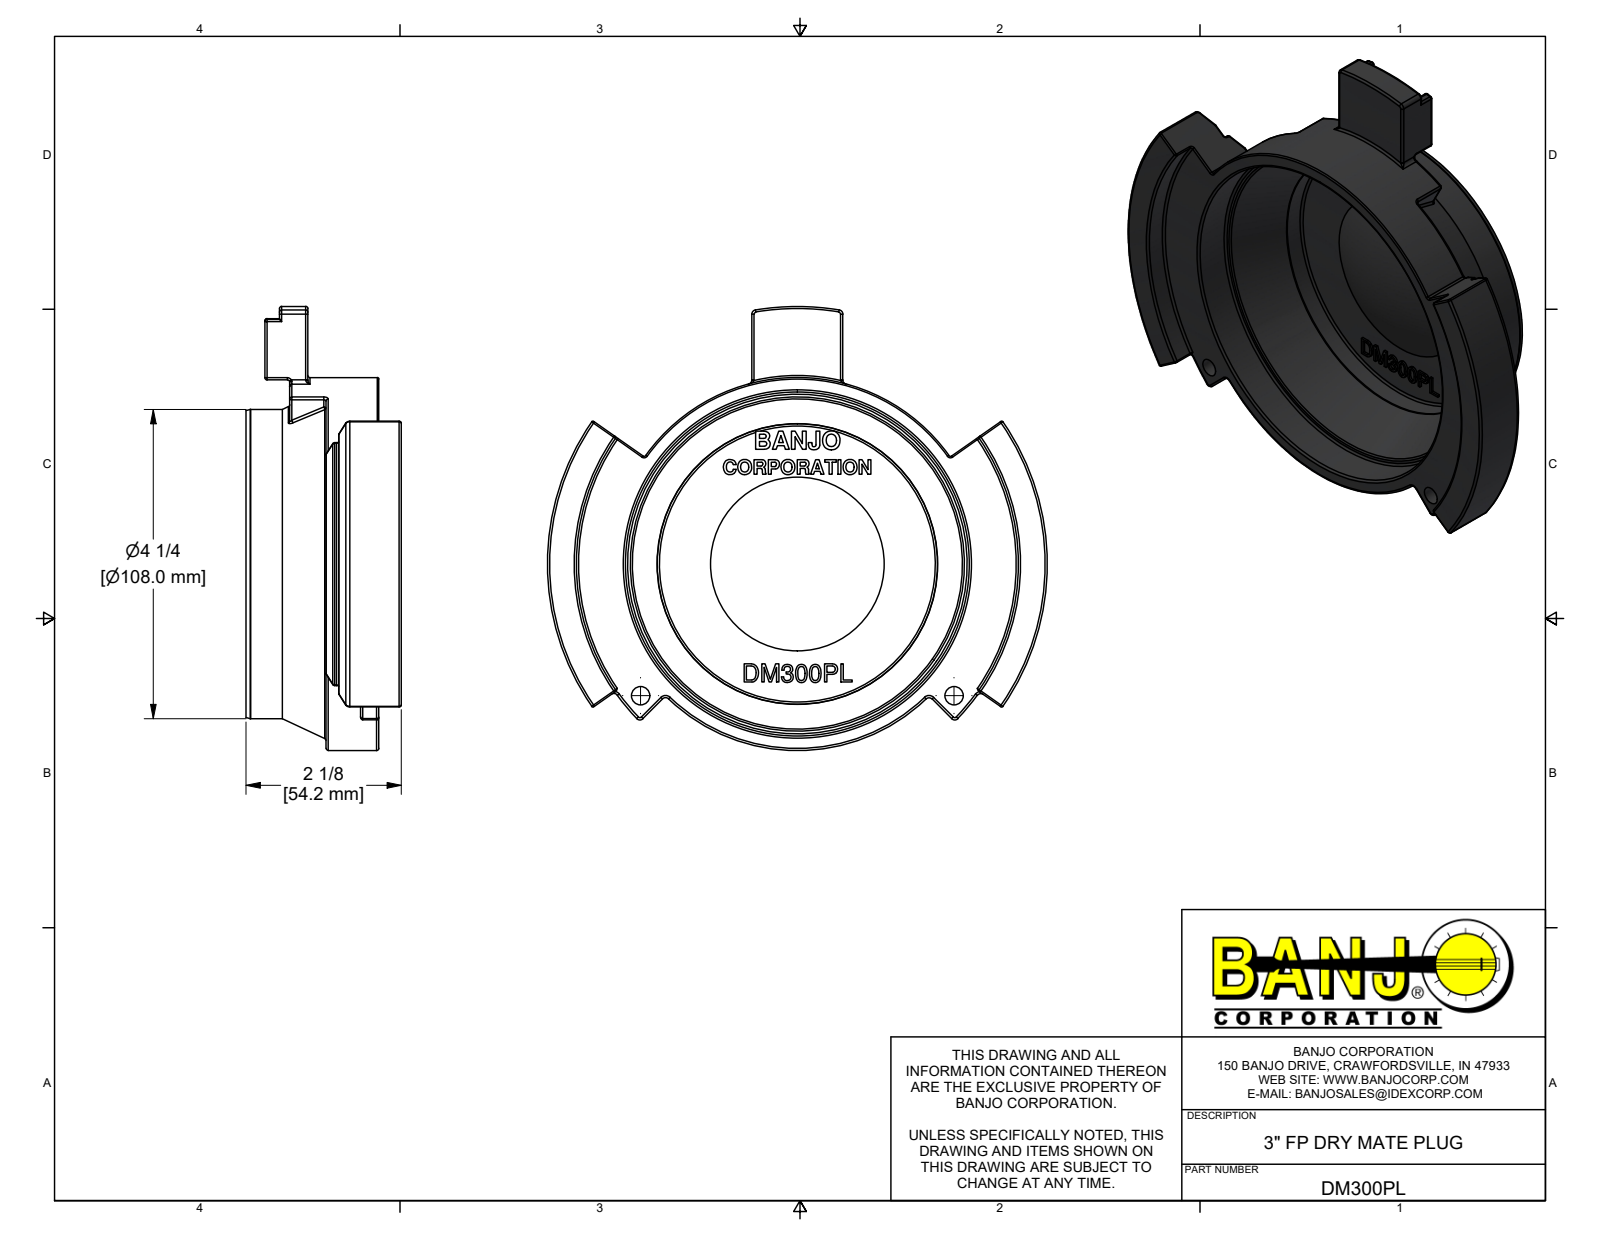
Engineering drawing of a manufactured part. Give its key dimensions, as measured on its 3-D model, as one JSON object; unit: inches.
{"part_name": "DM300PL", "step_written_by": "Autodesk Inventor 2022 (AUTOMOTIVE_DESIGN)", "units": "inches", "bodies": {"solids": 1, "faces": 602, "planar": 205, "cylindrical": 93, "other": 304}, "overall_size": [6.875, 6.103, 2.135], "volume_in3": 14.01, "surface_area_in2": 108.9, "round_holes": [[0.25, 2], [3.85, 1], [4.725, 1]], "round_bosses_or_shafts": [[4.25, 1]], "partial_cylinders_radius": [[0.03, 36], [0.02, 26], [0.06, 10], [2.562, 1], [2.6, 1], [2.925, 1], [3.038, 1], [3.062, 1]], "face_to_face_distances": [0.26, 1.565, 1.825, 0.31, 1.875, 2.135, 0.725, 0.84, 1.035, 1.1], "hole_center_spacings": [2.812, 4.309]}
